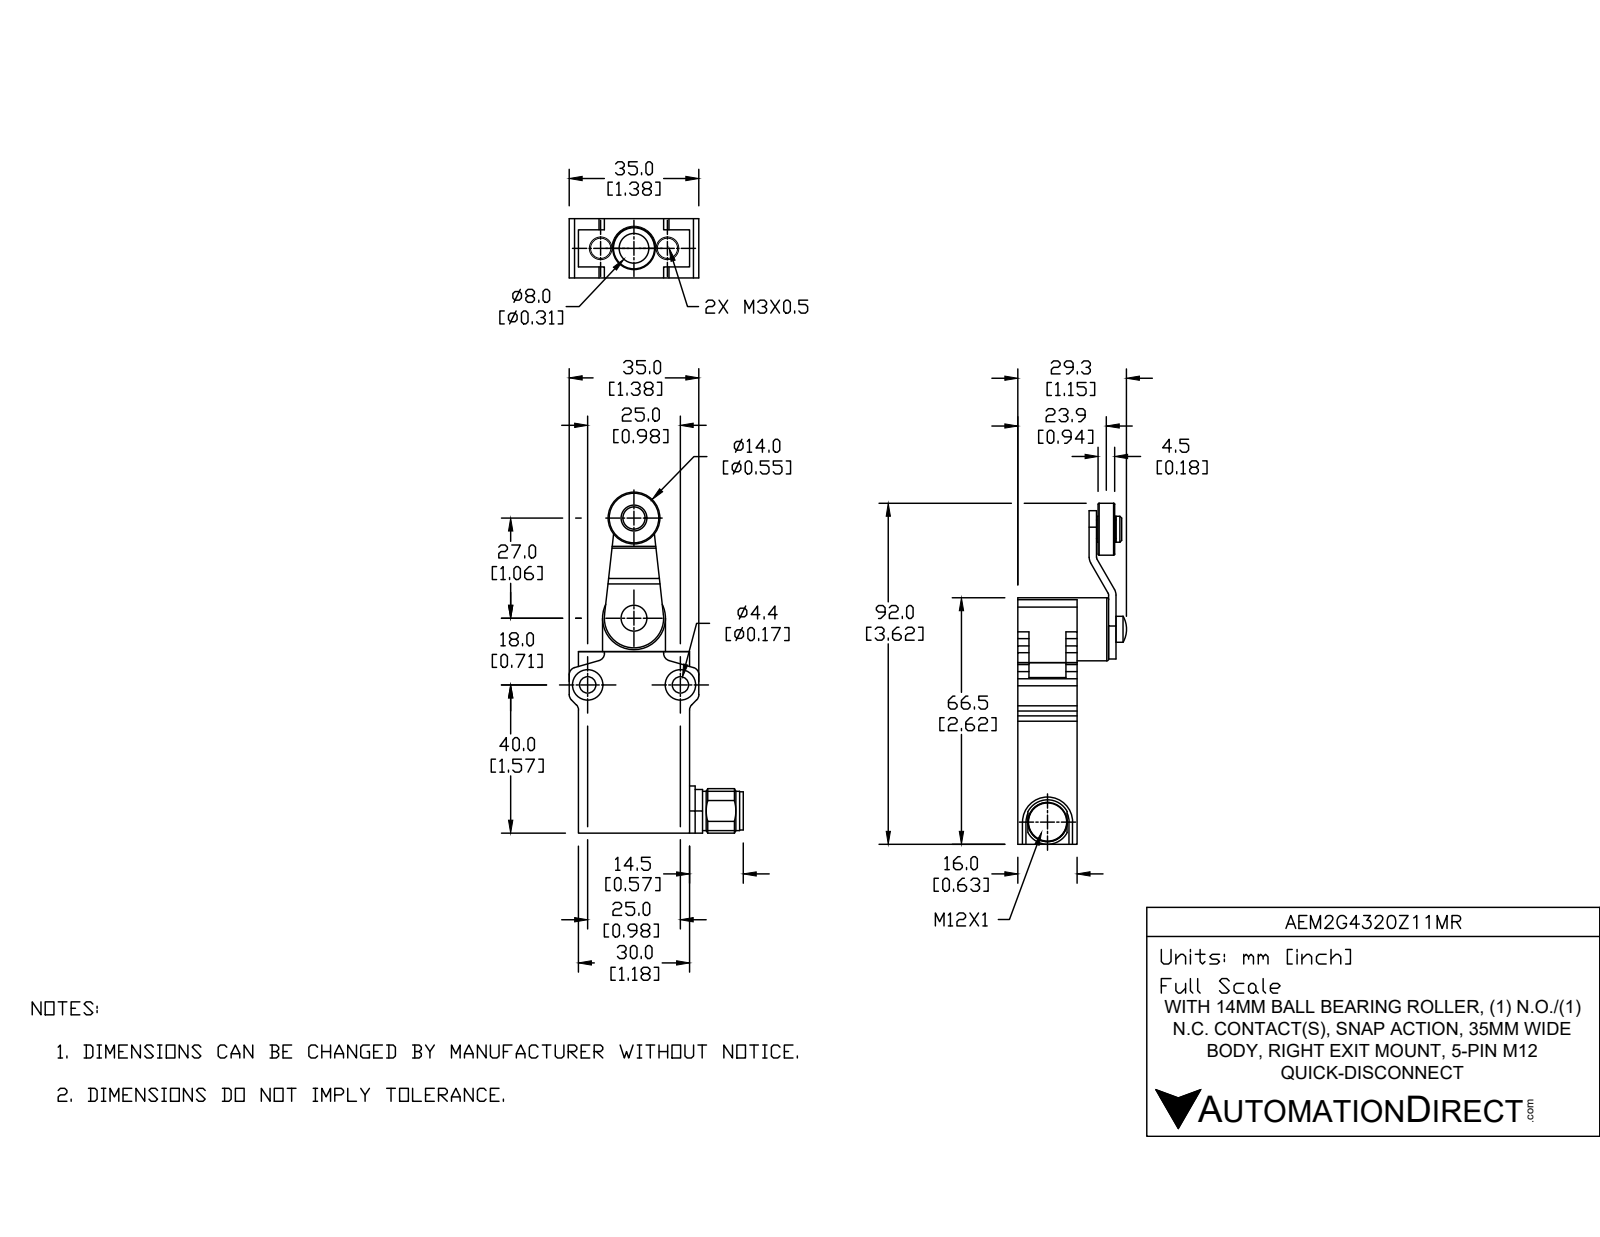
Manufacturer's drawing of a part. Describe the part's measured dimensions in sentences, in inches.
The part is named "AEM2G4320Z11MR". Its 3-D file was written by "SolidWorks 2019 (AUTOMOTIVE_DESIGN)". It is 7 solids with 545 faces: 299 planar, 61 cylindrical and 185 other. Overall it measures 3.72 by 1.831 by 1.26 inches. Its volume is 1.995 cubic inches and its surface area 18.48 square inches. Round holes: 2 of diameter 0.118, 2 of diameter 0.173, 2 of diameter 0.323, 1 of diameter 0.098, 1 of diameter 0.161, 1 of diameter 0.197, 1 of diameter 0.224. Round bosses or shafts: 2 of diameter 0.276, 1 of diameter 0.622, 1 of diameter 0.551, 1 of diameter 0.472, 1 of diameter 0.417, 1 of diameter 0.406, 1 of diameter 0.394, 1 of diameter 0.236. Partial cylindrical surfaces (rounded edges, fillets, slot ends): 8 of radius 0.079, 2 of radius 0.039, 2 of radius 0.118, 1 of radius 0.256, 1 of radius 0.315. The main face-to-face distances are 0.63, 1.181, 2.047, 0.354, 0.079, 0.984, 0.28, 0.902, 0.102, 0.472. The hole center spacings are 0.863, 1.82, 0.748, 0.984, 1.043.
